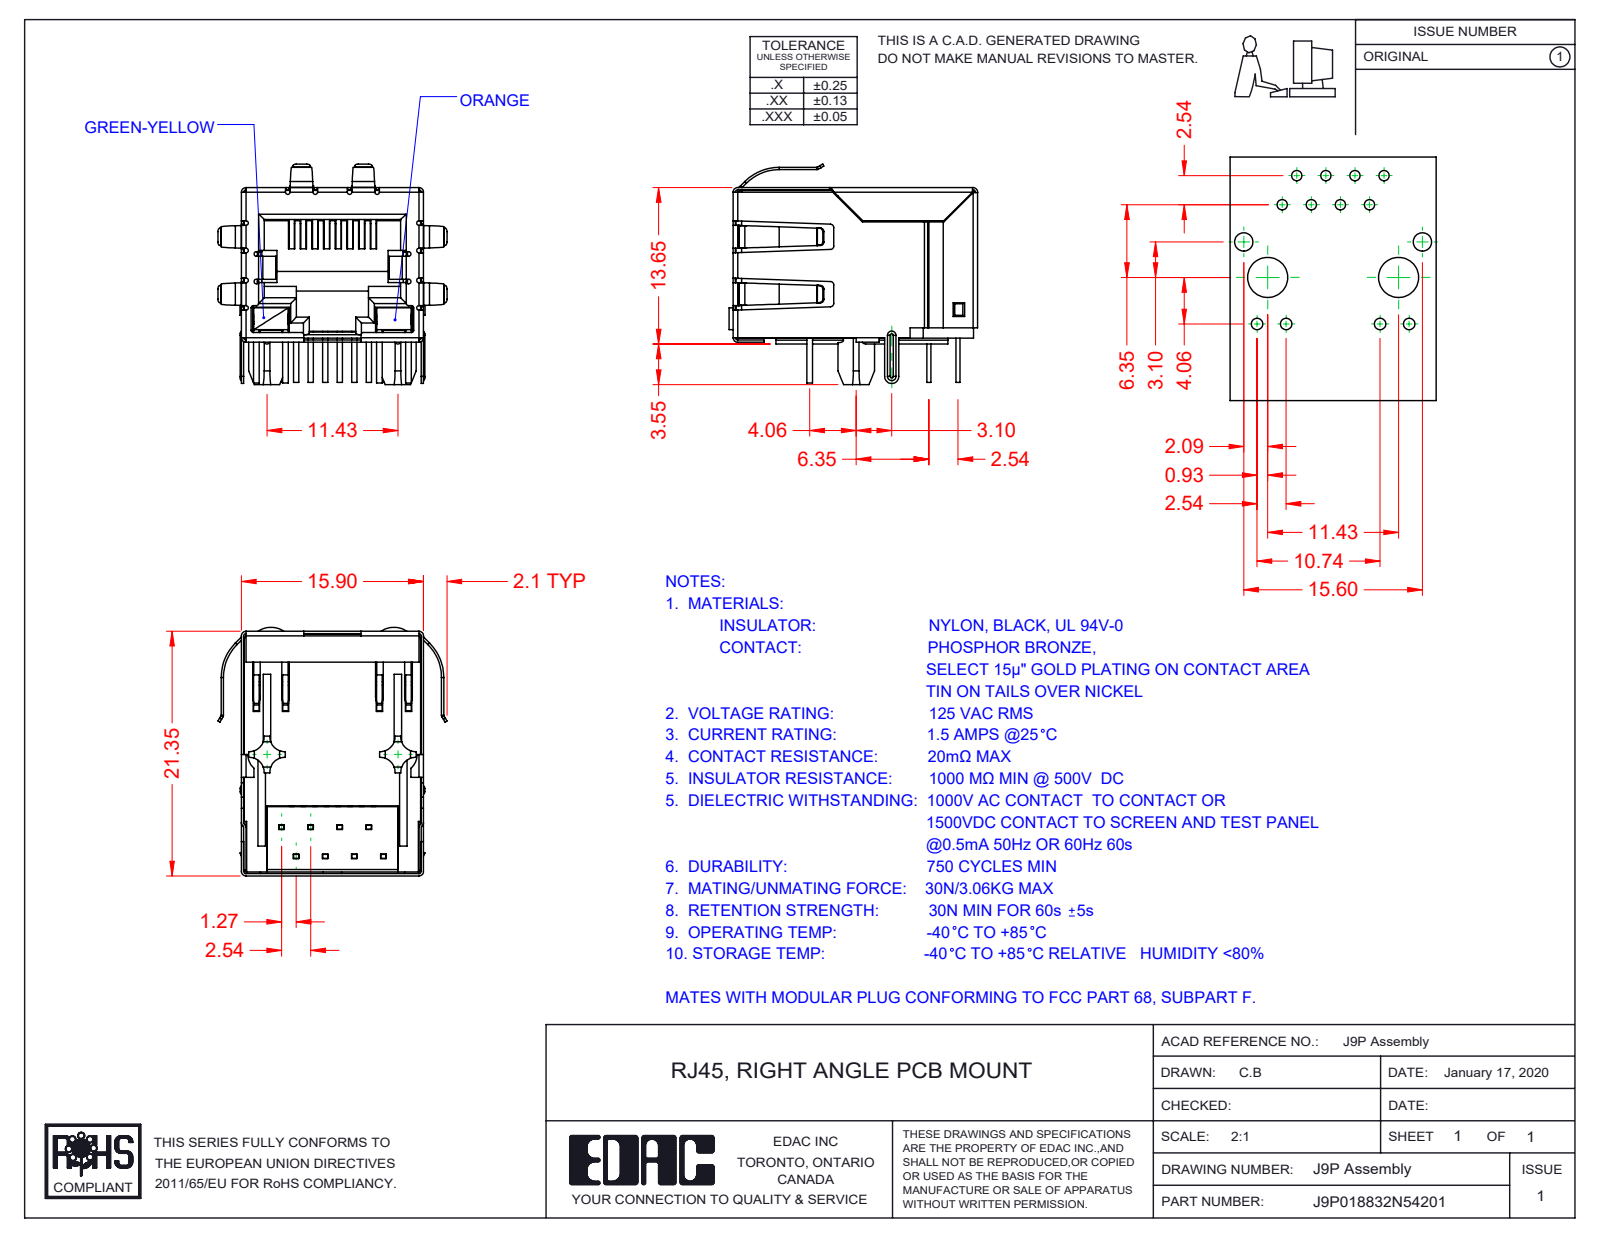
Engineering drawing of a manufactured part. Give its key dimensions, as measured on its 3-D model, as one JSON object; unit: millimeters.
{"part_name": "9P-LED Contact Lock; 9P-LED Insulator; 9P-LED Assembly; 9P-LED Shield (+4 more)", "step_written_by": "SolidWorks 2016 (CONFIG_CONTROL_DESIGN)", "units": "millimeters", "bodies": {"solids": 13, "faces": 1474, "planar": 1042, "cylindrical": 338, "other": 94}, "overall_size": [21.7, 20, 19.25], "volume_mm3": 2687, "surface_area_mm2": 7515, "partial_cylinders_radius": [[0.2, 39], [0.5, 22], [0.3, 20], [0.4, 16], [1.3, 8], [0.23, 5], [0.11, 4], [0.31, 4]], "face_to_face_distances": [15.45, 15.7, 15.65, 0.35, 0.54, 15.5, 12.36, 0.6, 1.4, 0.59]}
